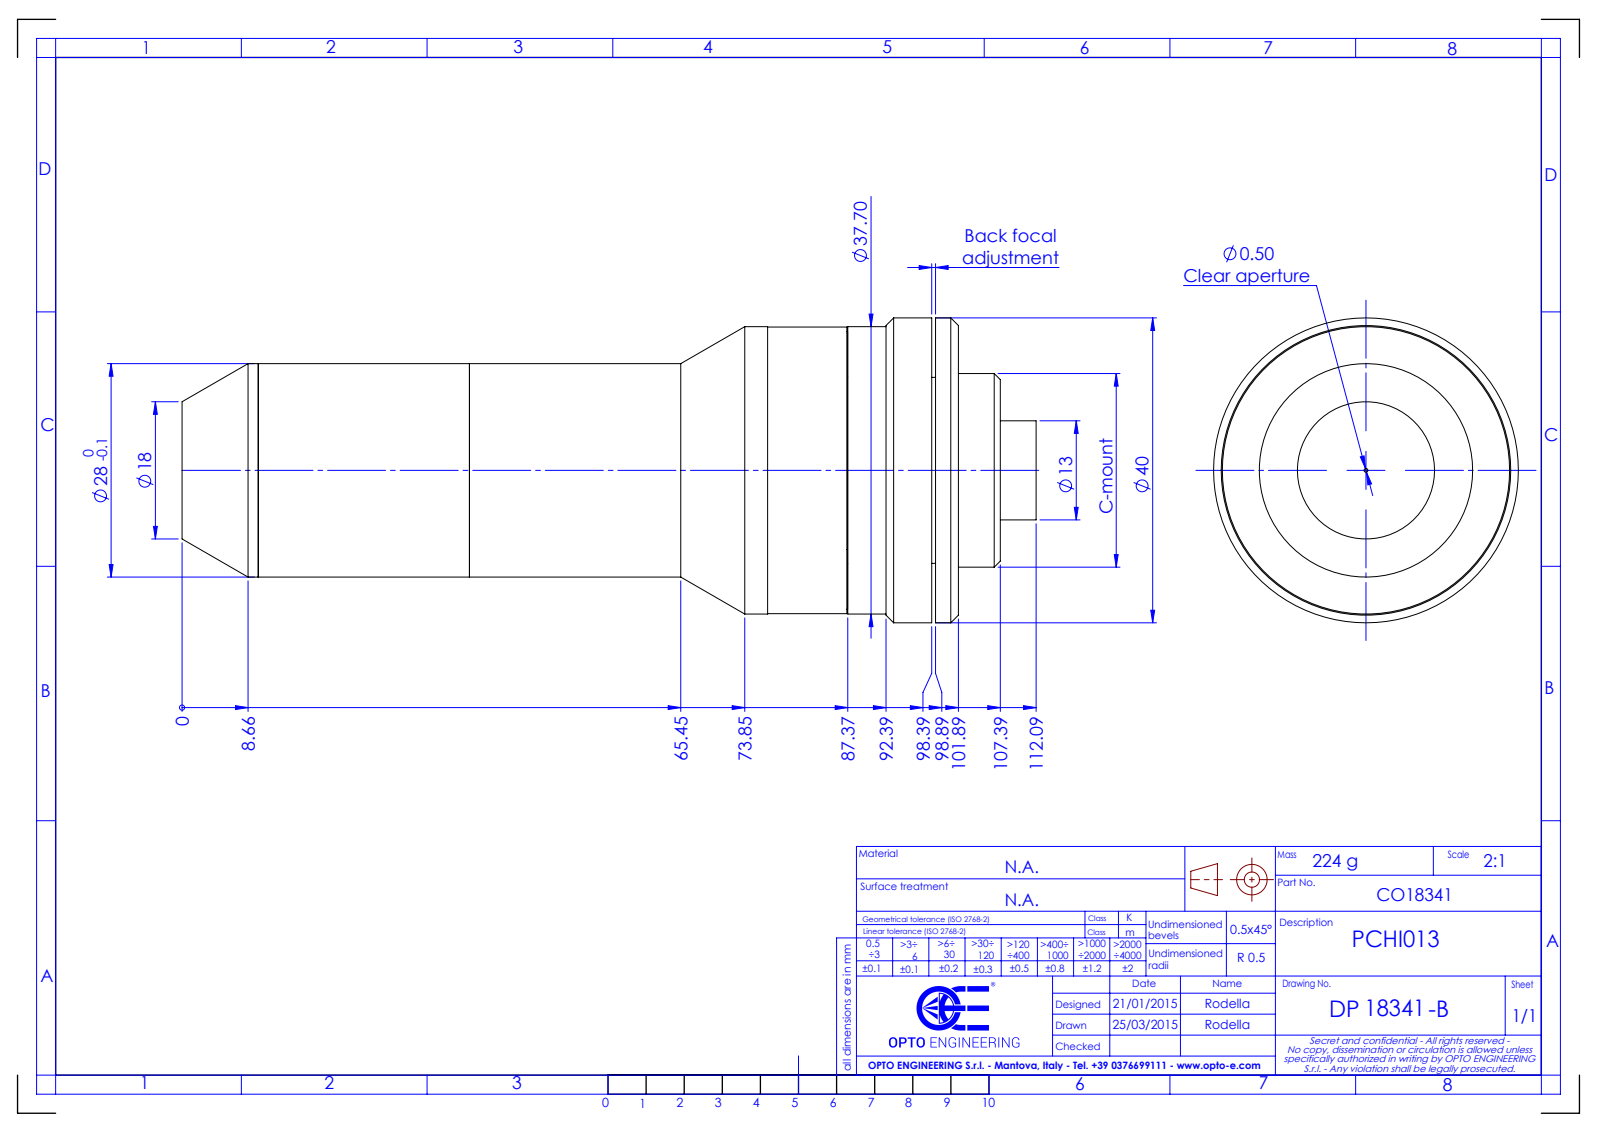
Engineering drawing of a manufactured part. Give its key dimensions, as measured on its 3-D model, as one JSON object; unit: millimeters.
{"part_name": "DP18341-B_PCHI013", "step_written_by": "SolidWorks 2021 (CONFIG_CONTROL_DESIGN)", "units": "millimeters", "bodies": {"solids": 0, "faces": 54, "planar": 14, "cylindrical": 26, "other": 14}, "overall_size": [112.09, 40, 40], "round_holes": [[6.5, 1], [22.5, 1]], "round_bosses_or_shafts": [[40, 1], [37.7, 1], [37.6, 1], [28, 1], [25.4, 1], [22, 1], [13, 1]], "face_to_face_distances": [0.5, 3.5, 3, 11.02, 11.52, 14.52, 8.5, 77.37, 88.39, 88.89]}
